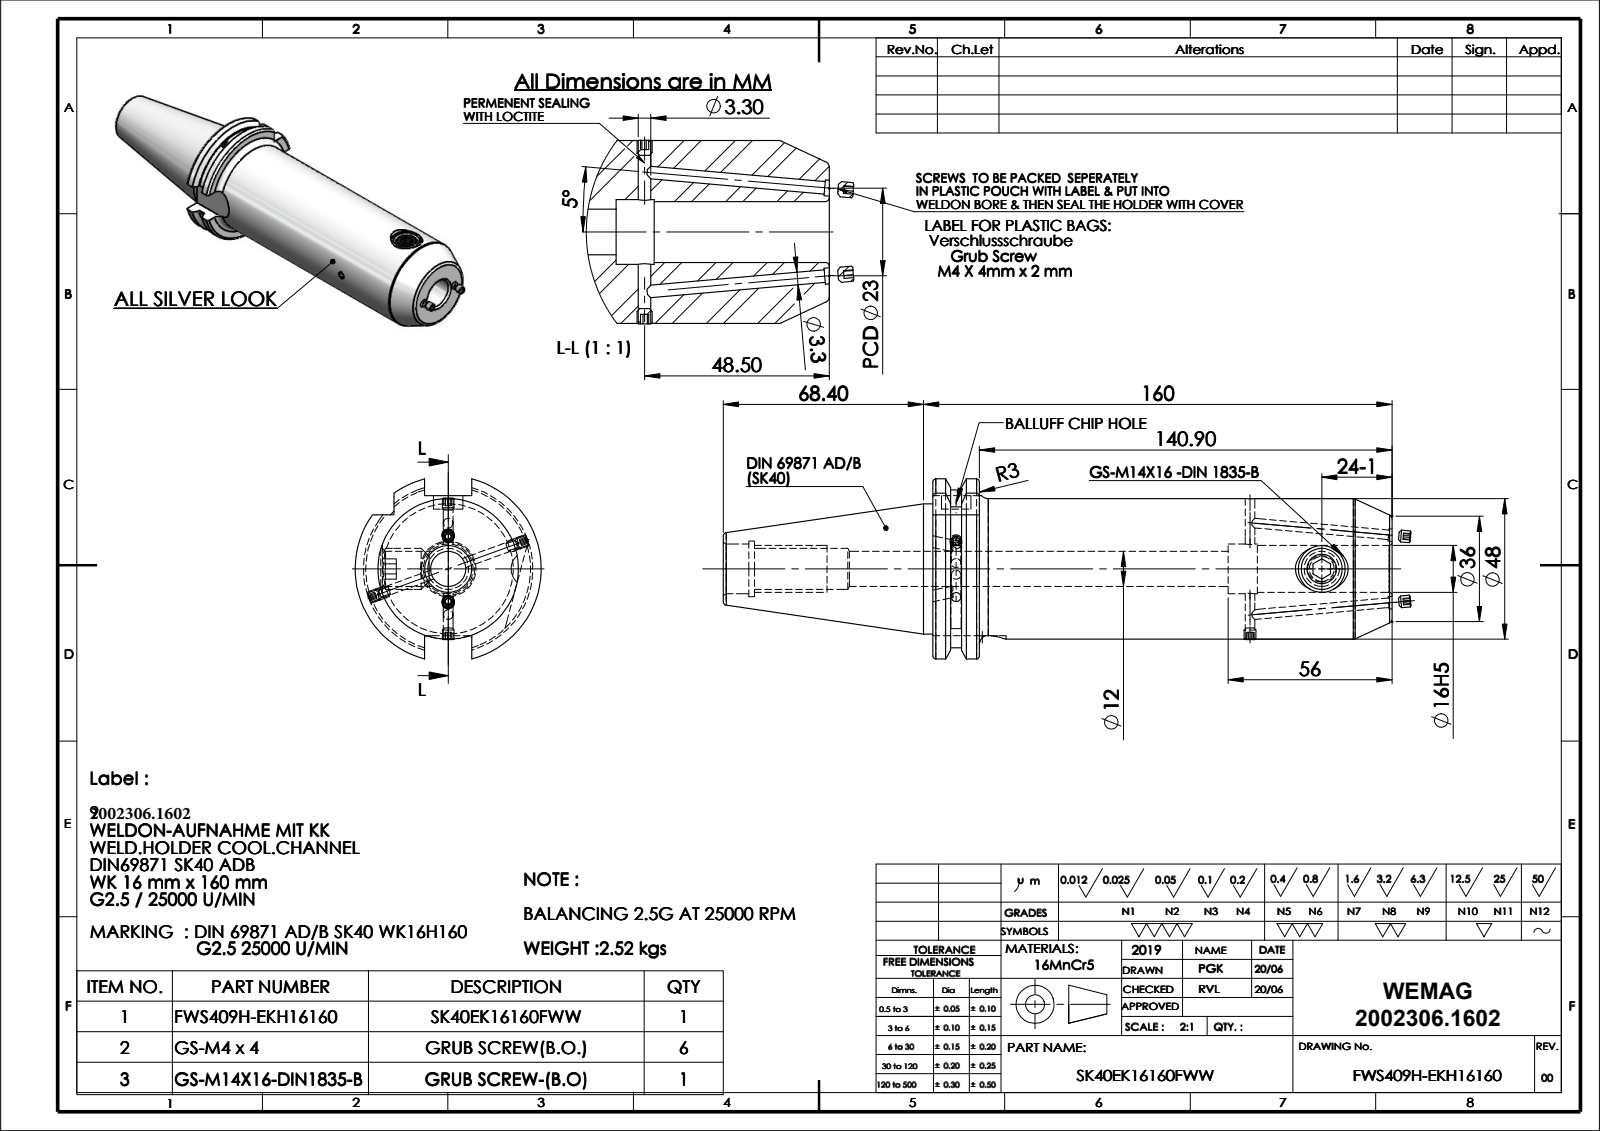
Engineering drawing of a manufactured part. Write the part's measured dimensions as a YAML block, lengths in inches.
part_name: "91406-WK216160"
step_written_by: "SolidWorks 2018 (CONFIG_CONTROL_DESIGN)"
units: inches
bodies: {solids: 1, faces: 137, planar: 40, cylindrical: 53, other: 44}
overall_size: [8.992, 2.502, 2.42]
volume: 19.87
surface_area: 75.95
round_holes:
  - {diameter: 0.13, count: 4}
  - {diameter: 0.165, count: 2}
  - {diameter: 0.472, count: 2}
  - {diameter: 0.63, count: 2}
  - {diameter: 0.394, count: 1}
  - {diameter: 0.551, count: 1}
  - {diameter: 0.669, count: 1}
  - {diameter: 0.748, count: 1}
round_bosses_or_shafts:
  - {diameter: 1.89, count: 1}
  - {diameter: 1.75, count: 1}
partial_cylinders:
  - {radius: 0.317, count: 1}
  - {radius: 1.107, count: 1}
  - {radius: 1.251, count: 1}
face_to_face_distances: [6.173, 0.626, 5.547, 1.882, 0.634, 2.819, 3.445, 8.992, 0.421, 2.398]
hole_center_spacings: [3.951]
